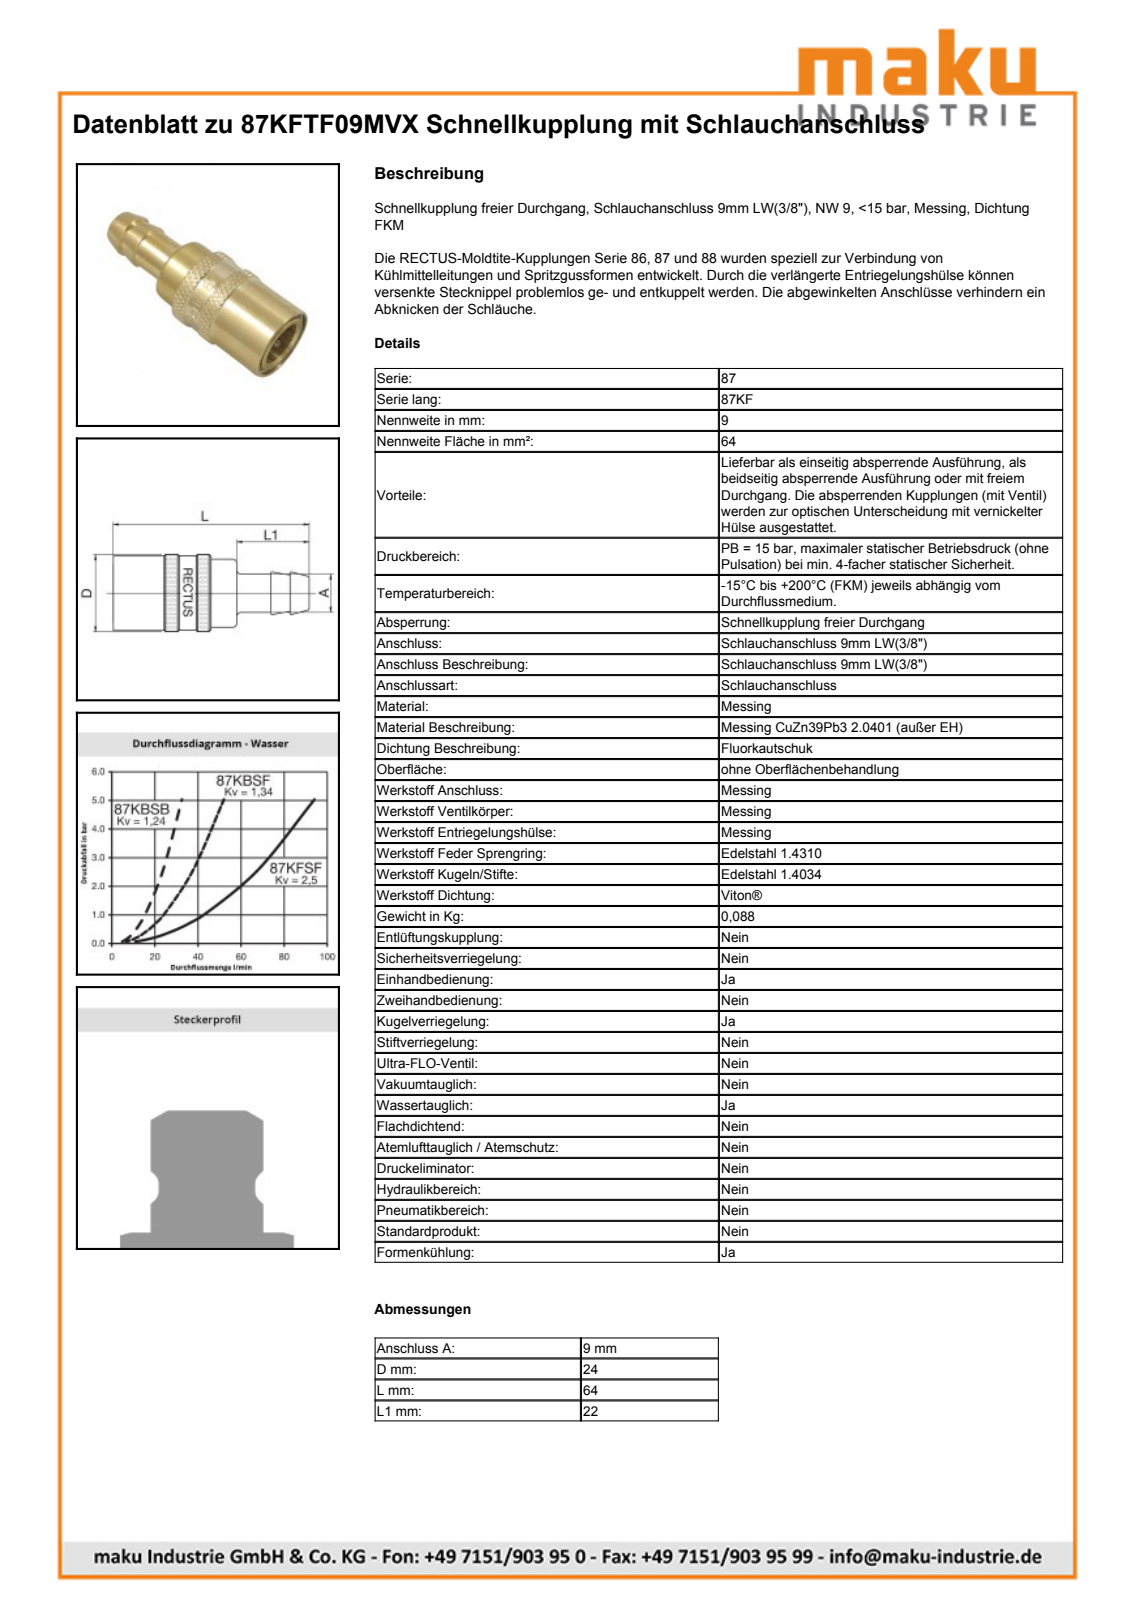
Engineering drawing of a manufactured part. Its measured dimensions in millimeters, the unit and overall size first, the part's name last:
Units: millimetres
Overall size (bounding box): 63.6 × 24.15 × 24.15
Round holes (diameter × count): ⌀16 ×1, ⌀17.5 ×1, ⌀18.75 ×1, ⌀21.05 ×1, ⌀21.25 ×1
Round bosses / shafts (diameter × count): ⌀24.15 ×1, ⌀23 ×1, ⌀20.5 ×1, ⌀18 ×1, ⌀17.25 ×1, ⌀16.45 ×1, ⌀15.54 ×1, ⌀9.5 ×1
Partial cylindrical surfaces — rounded edges, fillets, slot ends (radius × count): R11.4 ×1
Main face-to-face distances: 41.6, 30.25, 11.35, 20, 10.25, 21.6, 9.1, 10.9, 21.15, 32.5
Volume: 16 596 mm³ · Surface area: 10 115 mm²
Bodies: 2 solids, 452 faces (140 planar, 60 cylindrical, 252 other)
Part name (STEP PRODUCT): D108524
STEP written by: Autodesk Inventor 2013 (AUTOMOTIVE_DESIGN)
